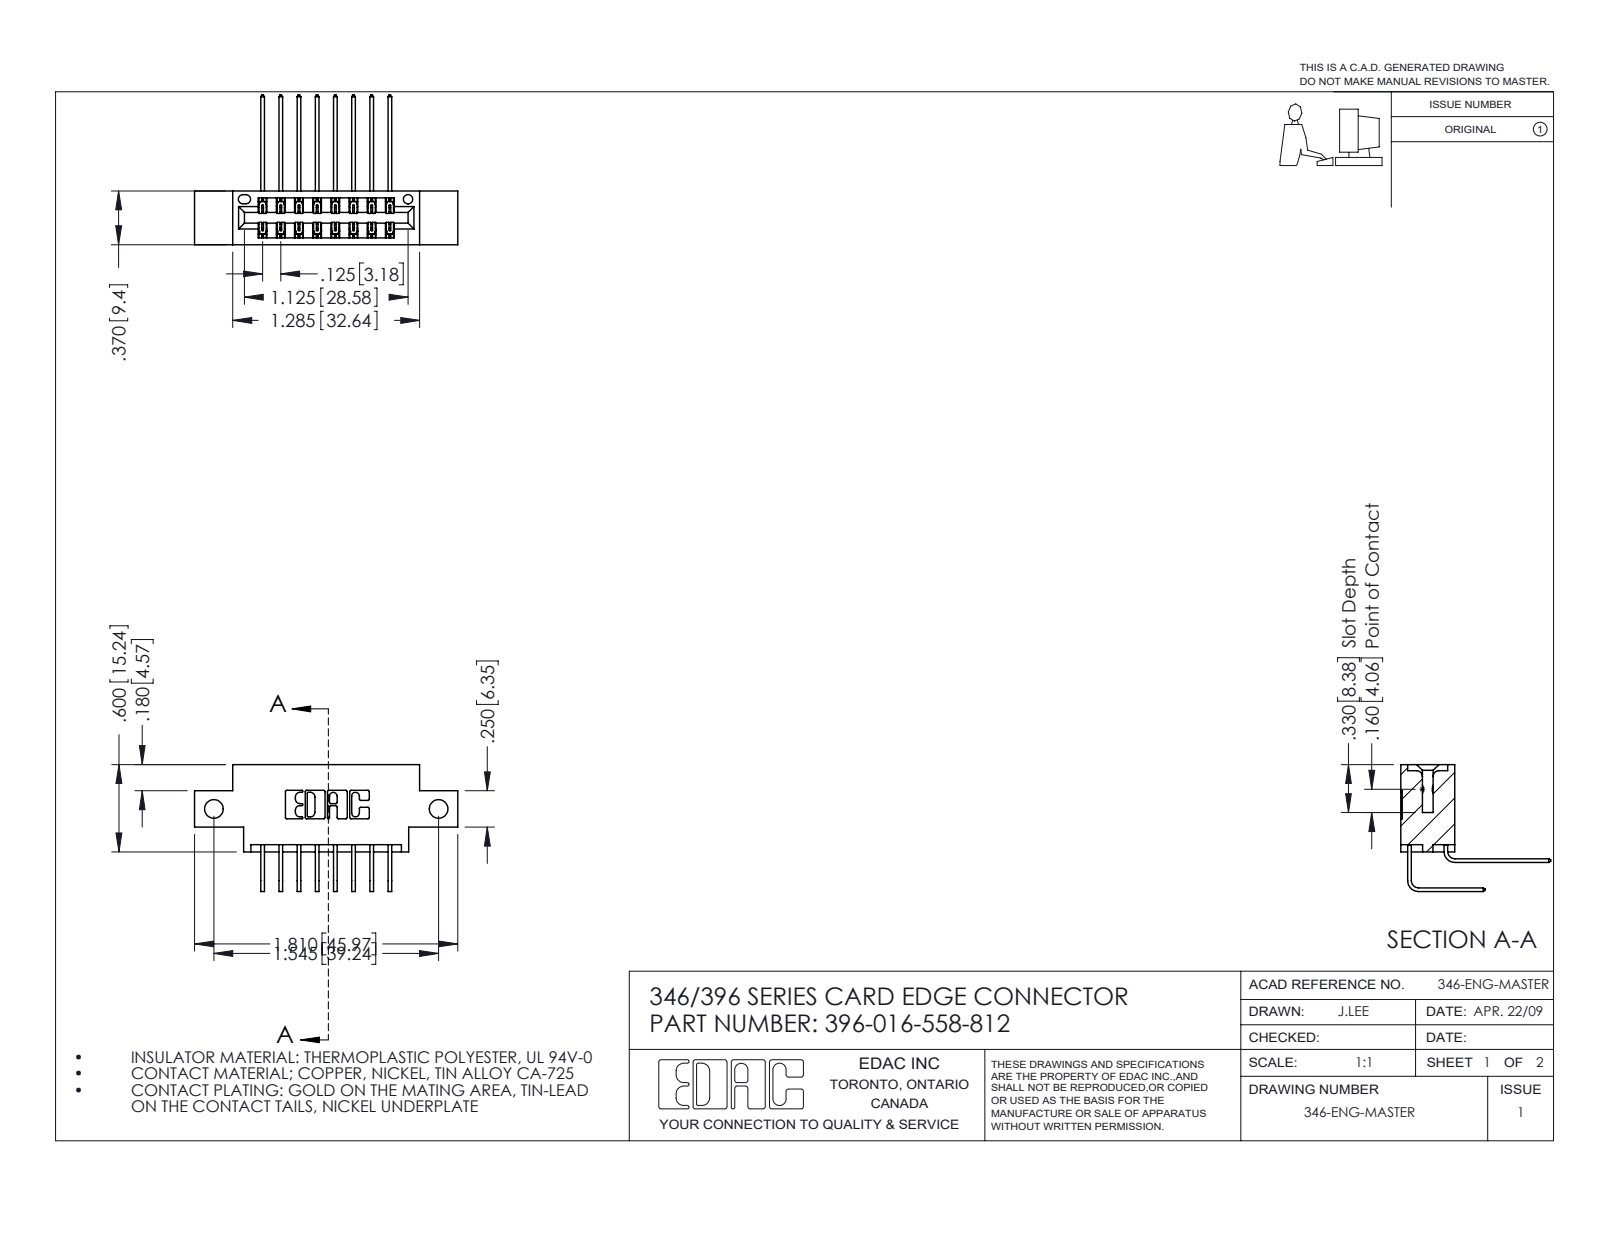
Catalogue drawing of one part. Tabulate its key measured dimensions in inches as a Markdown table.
| quantity | value |
| --- | --- |
| part name | 345-292-001_558 559 Tail - 1; 396-016-558-812; 345-292-001_558 Tail - 2; 346 Part_0.170 Offset - Side Mount |
| STEP written by | SolidWorks 2016 (CONFIG_CONTROL_DESIGN) |
| units | inches |
| bodies | 17 solids, 990 faces (672 planar, 318 cylindrical, 0 other) |
| overall size | 1.81 × 1.03 × 0.873 |
| volume | 0.248 in³ |
| surface area | 8.594 in² |
| round holes (diameter × count) | 0.128 × 2, 0.064 × 1 |
| partial cylindrical surfaces (radius × count) | 0.006 × 24, 0.01 × 22, 0.007 × 6, 0.031 × 6, 0.026 × 3, 0.014 × 2, 0.022 × 2, 0.024 × 2 |
| main face-to-face distances | 0.25, 0.048, 0.322, 0.37, 0.025, 0.072, 0.298, 0.148, 0.222, 0.1 |
| hole center spacings | 1.545 |
